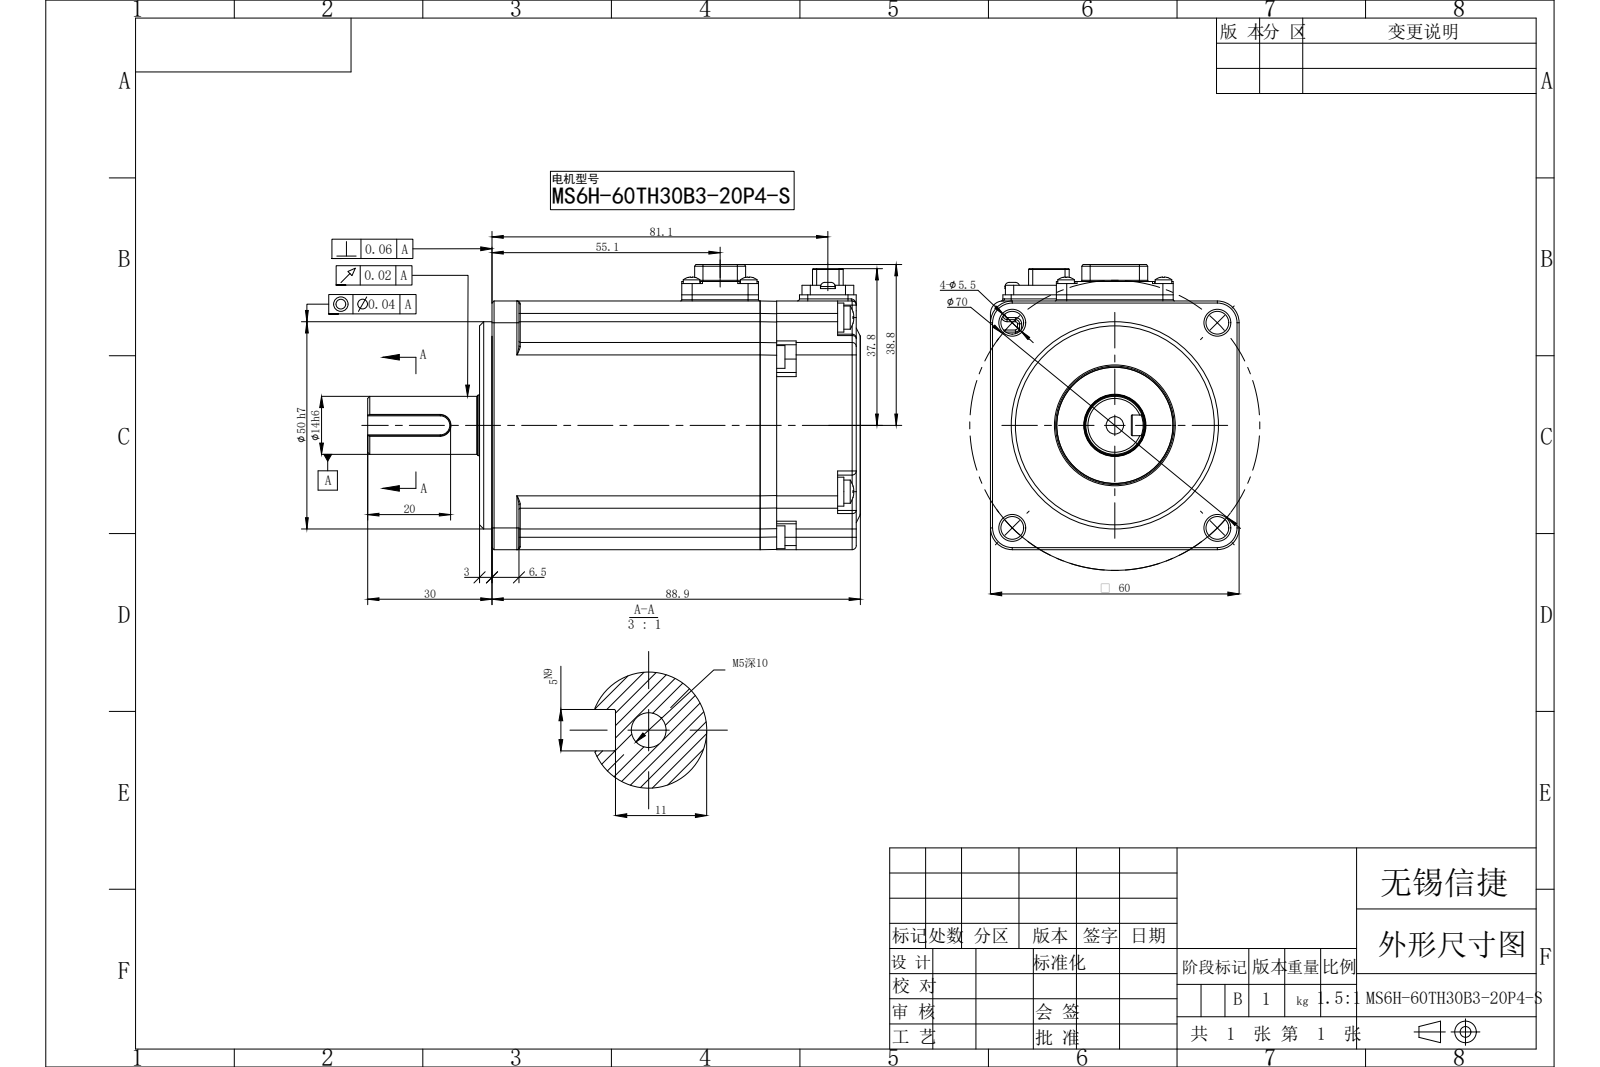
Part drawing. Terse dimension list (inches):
name: MS6H-60TH30B3-20P4-S
written by: SolidWorks 2022 (CONFIG_CONTROL_DESIGN)
unit: in
bodies: 0 solids, 814 faces (400 planar, 266 cylindrical, 148 other)
size: 4.681 × 2.709 × 2.362
holes: 4× ⌀0.083, 4× ⌀0.217, 2× ⌀0.063, 1× ⌀0.165, 1× ⌀0.591
bosses: 4× ⌀0.276, 4× ⌀0.22, 4× ⌀0.217, 4× ⌀0.157, 2× ⌀0.138, 1× ⌀1.969, 1× ⌀1.102, 1× ⌀0.583
rounds: 39× R0.039, 24× R0.02, 22× R0.012, 19× R0.008, 17× R0.118, 12× R0.079, 8× R0.018, 8× R0.197
face distances: 2.362, 3.618, 0.118, 3.5, 2.547, 0.394, 3.461, 1.969, 0.039, 3.579
hole spacings: 1.378, 1.949, 0.315, 0.654, 0.726, 2.756, 0.881, 0.925
